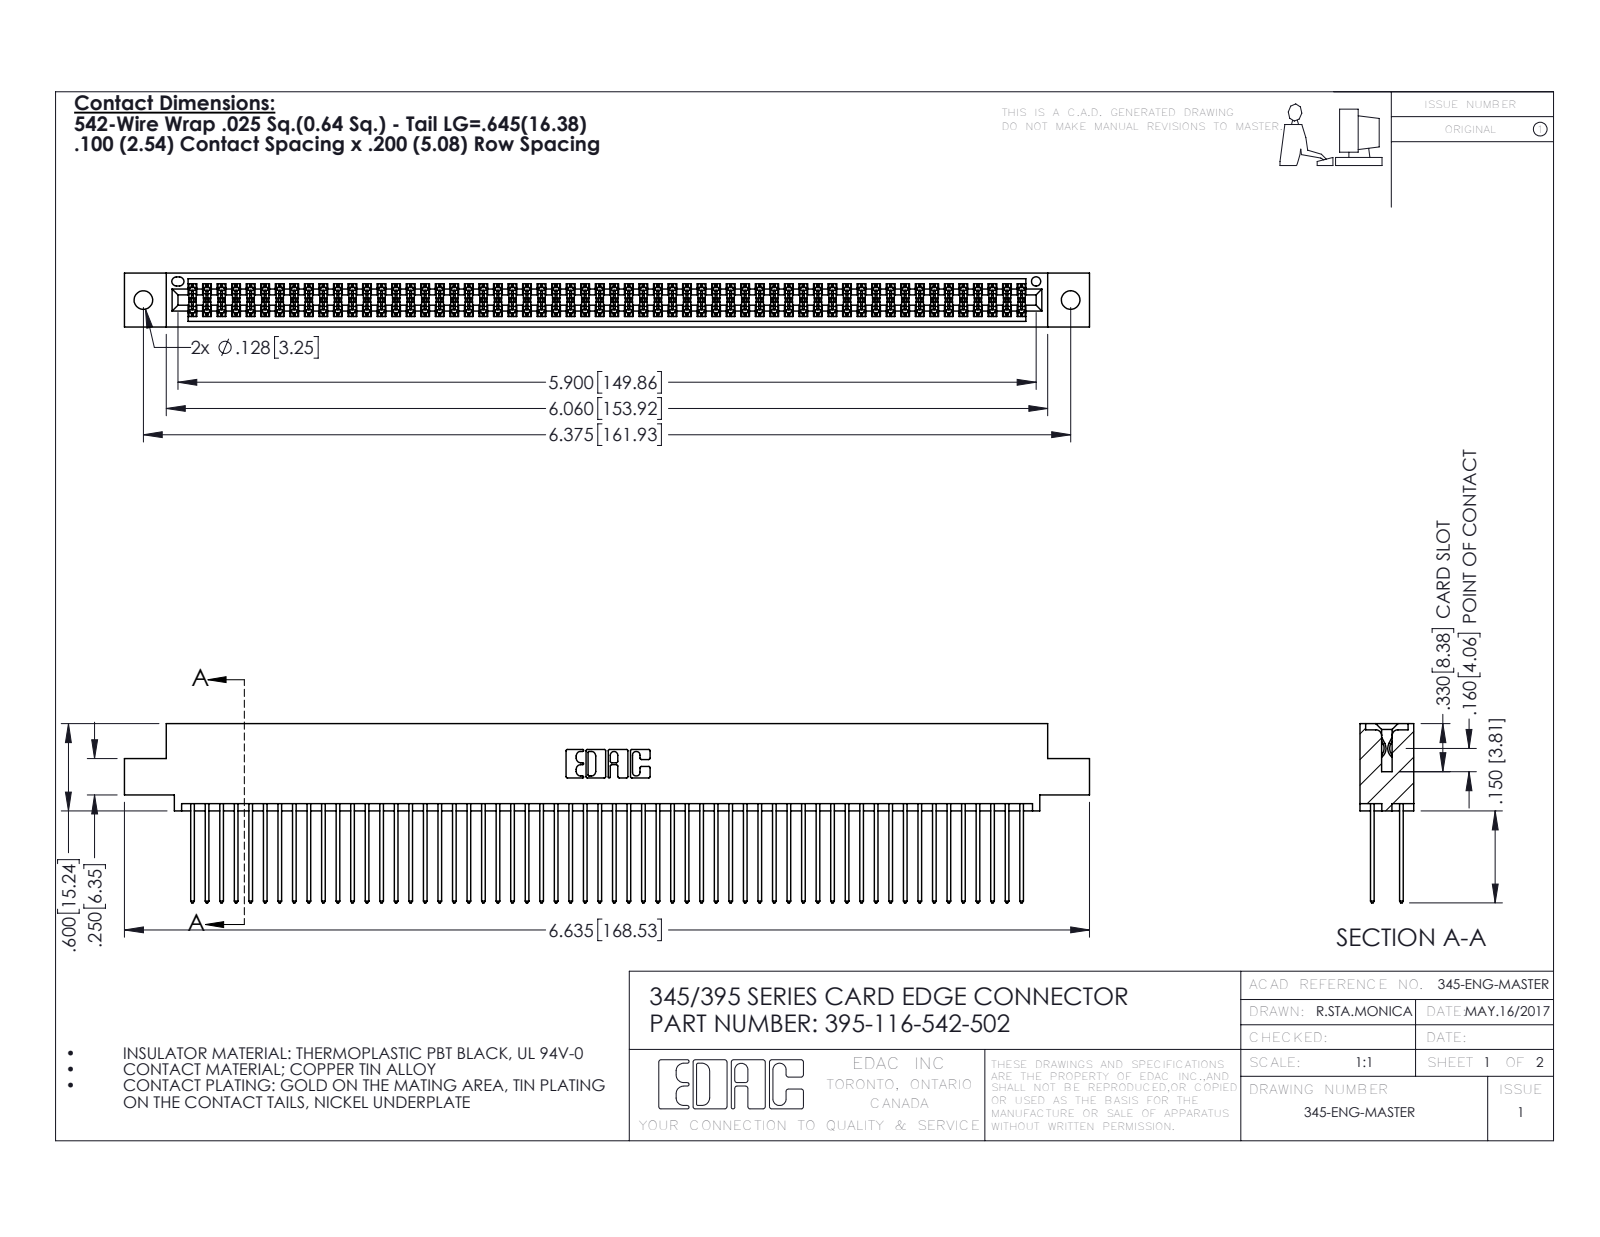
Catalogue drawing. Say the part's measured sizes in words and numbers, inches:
The part is named "345-292-001_345-293-142; 345 Part_0.110 Offset - 0.128 Dia; 395-116-542-502". Its 3-D file was written by "SolidWorks 2016 (CONFIG_CONTROL_DESIGN)". It is 117 solids with 5930 faces: 3912 planar, 2018 cylindrical and 0 other. Overall it measures 6.635 by 1.232 by 0.37 inches. Its volume is 1.034 cubic inches and its surface area 42.95 square inches. Round holes: 2 of diameter 0.128, 1 of diameter 0.064. Partial cylindrical surfaces (rounded edges, fillets, slot ends): 174 of radius 0.006, 116 of radius 0.01, 22 of radius 0.01, 6 of radius 0.007, 6 of radius 0.031, 3 of radius 0.026, 2 of radius 0.014, 2 of radius 0.019. The main face-to-face distances are 0.298, 0.072, 0.2, 0.098, 0.272, 0.025, 0.225, 0.37, 0.175, 0.149. The hole center spacings are 0.27, 6.139, 6.375.
